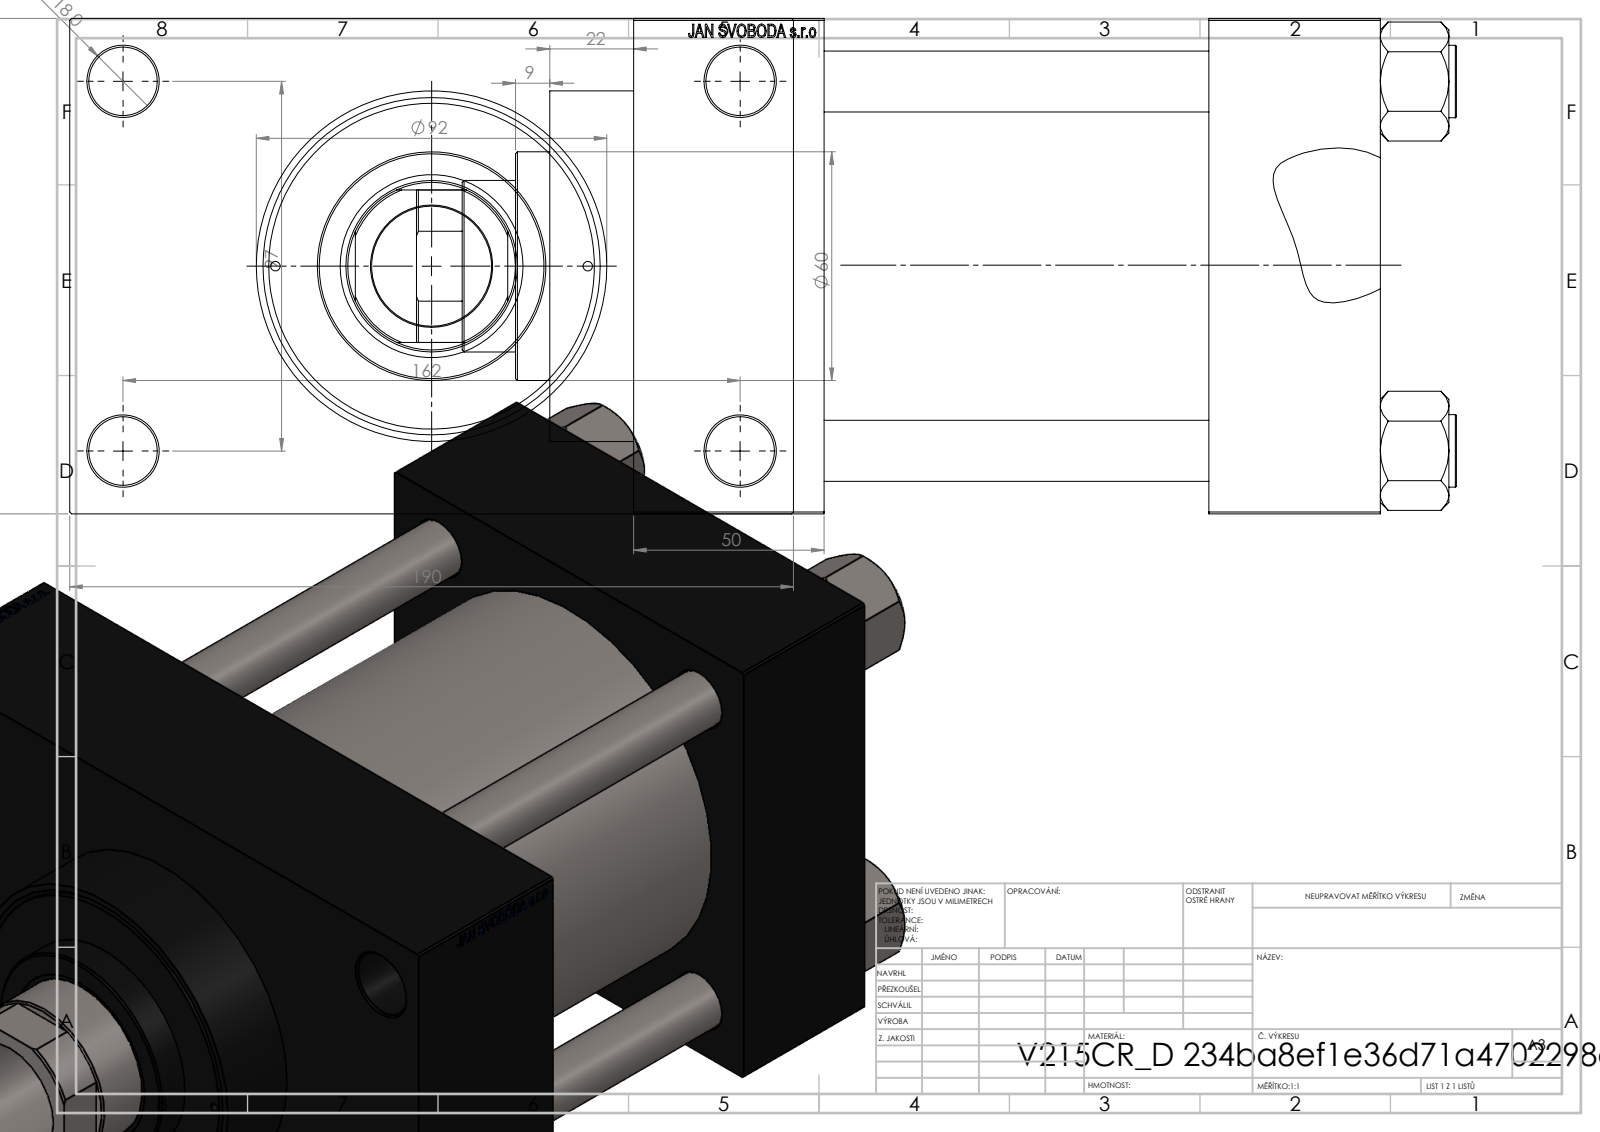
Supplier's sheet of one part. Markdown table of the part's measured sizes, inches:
| quantity | value |
| --- | --- |
| part name | V215_VC_A; V215CR_D_Body; V215CR_VCP_D; NUT_M5_D (+1 more) |
| STEP written by | SolidWorks 2019 (CONFIG_CONTROL_DESIGN) |
| units | inches |
| bodies | 11 solids, 1159 faces (547 planar, 92 cylindrical, 520 other) |
| overall size | 10.748 × 7.48 × 5.118 |
| volume | 164.2 in³ |
| surface area | 595.8 in² |
| round holes (diameter × count) | 0.63 × 4, 0.709 × 4, 0.098 × 2, 0.276 × 2, 1.041 × 2, 1.378 × 2, 1.24 × 1, 1.772 × 1, 1.89 × 1, 2.992 × 1, 3.366 × 1, 3.937 × 1 |
| round bosses / shafts (diameter × count) | 0.748 × 4, 4.173 × 1, 3.622 × 1, 2.362 × 1 |
| partial cylindrical surfaces (radius × count) | 0.866 × 1 |
| main face-to-face distances | 1.969, 5.118, 1.772, 5.748, 3.976, 7.717, 5.945, 1.181, 6.299, 3.78 |
| hole center spacings | 1.281, 1.93, 2.475, 2.698, 3.717, 3.815, 4.005, 4.026 |
